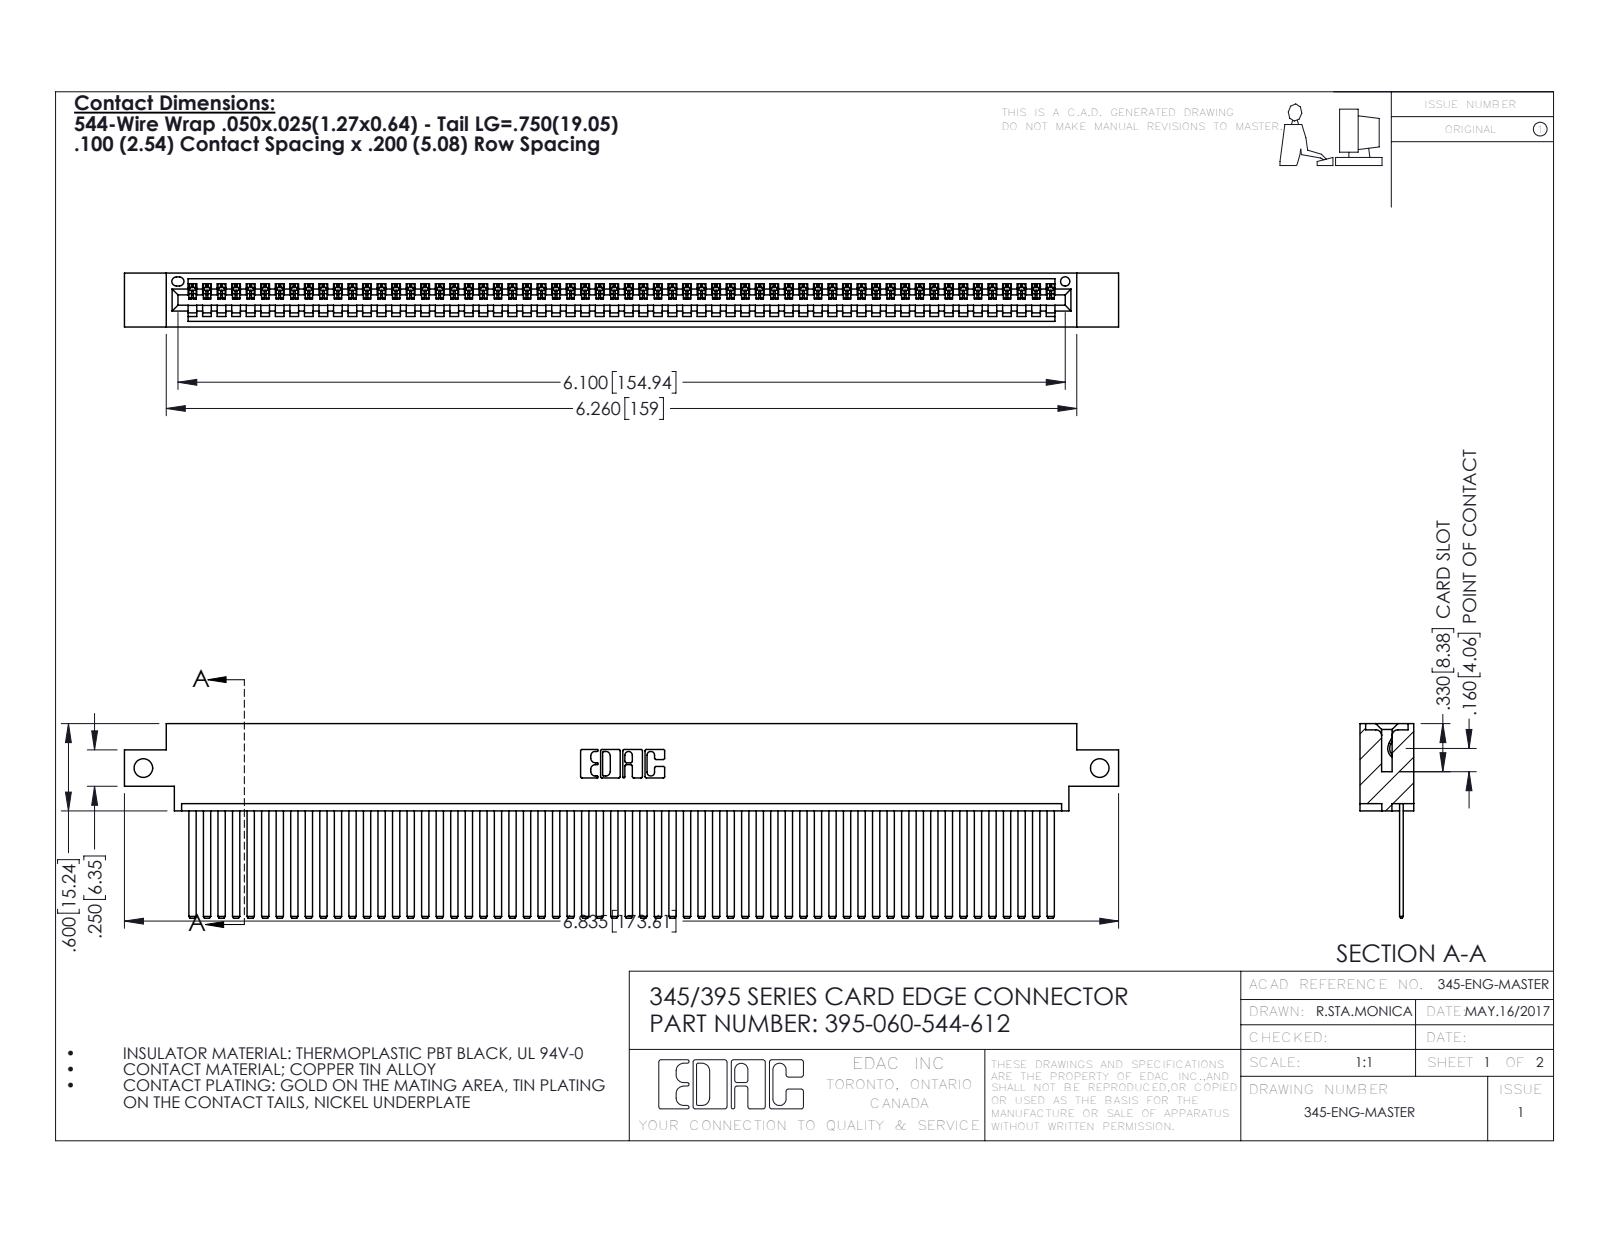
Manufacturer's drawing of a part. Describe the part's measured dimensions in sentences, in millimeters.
The part is named "395-060-544-612; 345-292-001_345-293-144; 345 Part_0.170 Offset - Side Mount". Its 3-D file was written by "SolidWorks 2016 (CONFIG_CONTROL_DESIGN)". It is 61 solids with 3250 faces: 2244 planar, 1006 cylindrical and 0 other. Overall it measures 173.6 by 34 by 9.4 millimeters. Its volume is 17 120 cubic millimeters and its surface area 25 080 square millimeters. Round holes: 2 of diameter 3.3, 1 of diameter 1.6. Partial cylindrical surfaces (rounded edges, fillets, slot ends): 120 of radius 0.2, 22 of radius 0.3, 6 of radius 0.2, 6 of radius 0.8, 3 of radius 0.7, 2 of radius 0.8, 2 of radius 1, 1 of radius 0.4. The main face-to-face distances are 1.8, 7.6, 0.6, 2.5, 6.9, 9.4, 5.1, 5.7, 4.4, 3.8. The hole center spacings are 167.
